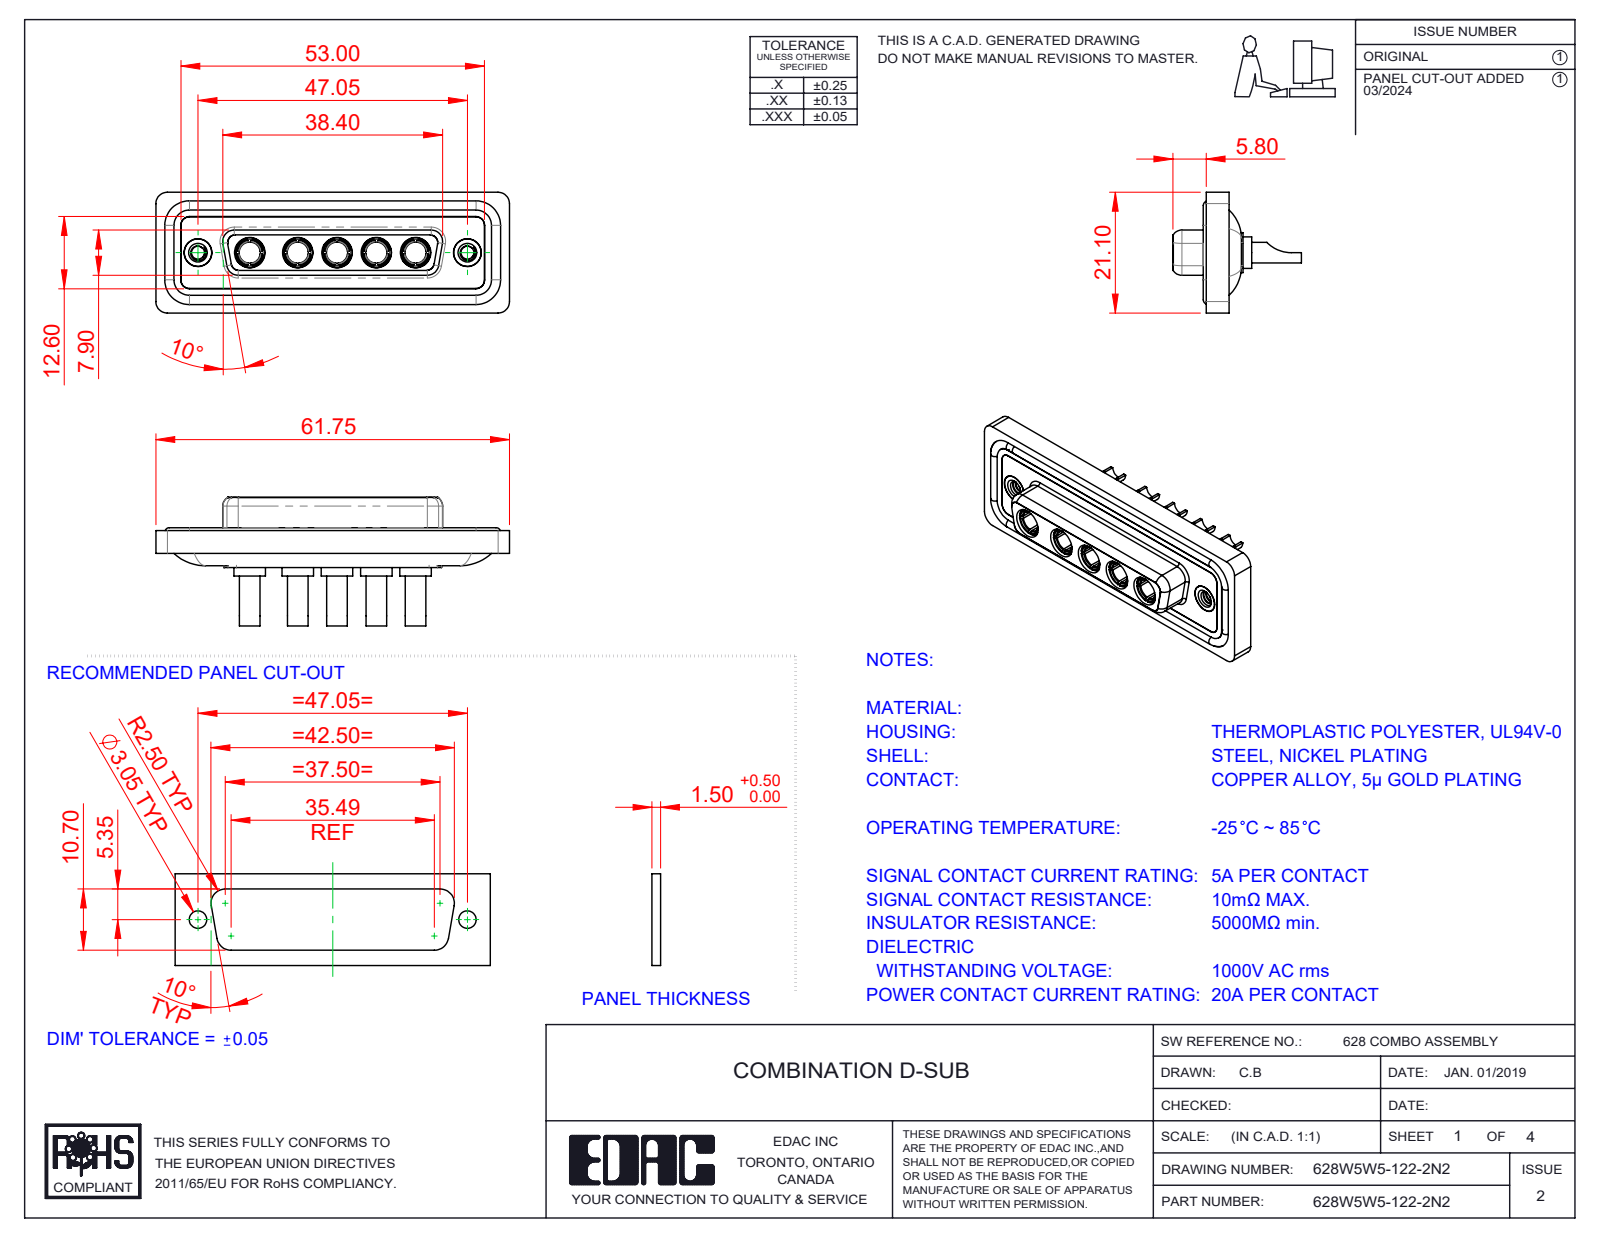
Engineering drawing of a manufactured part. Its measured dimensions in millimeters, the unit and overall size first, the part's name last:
Units: millimetres
Overall size (bounding box): 61.75 × 22.45 × 21.1
Round holes (diameter × count): ⌀4.85 ×7, ⌀2.7 ×5, ⌀3.7 ×5, ⌀5.3 ×5, ⌀2.26 ×2, ⌀4 ×2, ⌀4.05 ×2, ⌀5 ×2
Round bosses / shafts (diameter × count): ⌀5.5 ×5, ⌀5.2 ×5, ⌀4.96 ×5, ⌀4.75 ×5, ⌀3.75 ×5, ⌀3.6 ×5, ⌀1.6 ×4, ⌀4.95 ×2
Partial cylindrical surfaces — rounded edges, fillets, slot ends (radius × count): R1.5 ×22, R2 ×18, R1.35 ×8, R1.6 ×8, R2.1 ×5, R0.25 ×4, R0.5 ×4, R0.6 ×4
Main face-to-face distances: 0.4, 1.8, 7.45, 5.65, 0.5, 7.05, 6.6, 1.6, 1.1, 2.9
Hole centre spacings: 6.86, 9.04, 13.72, 38.01, 8.39, 15.25, 15.9, 17.43
Volume: 8 237 mm³ · Surface area: 13 828 mm²
Bodies: 17 solids, 786 faces (265 planar, 318 cylindrical, 203 other)
Part name (STEP PRODUCT): 628Combo Waterproof Housing_25 Contacts; 628Combo Threaded Rivet_2; 628Combo Housing_5W5; 628Combo Shell Front_25 Contacts (+3 more)
STEP written by: SolidWorks 2023 (CONFIG_CONTROL_DESIGN)
